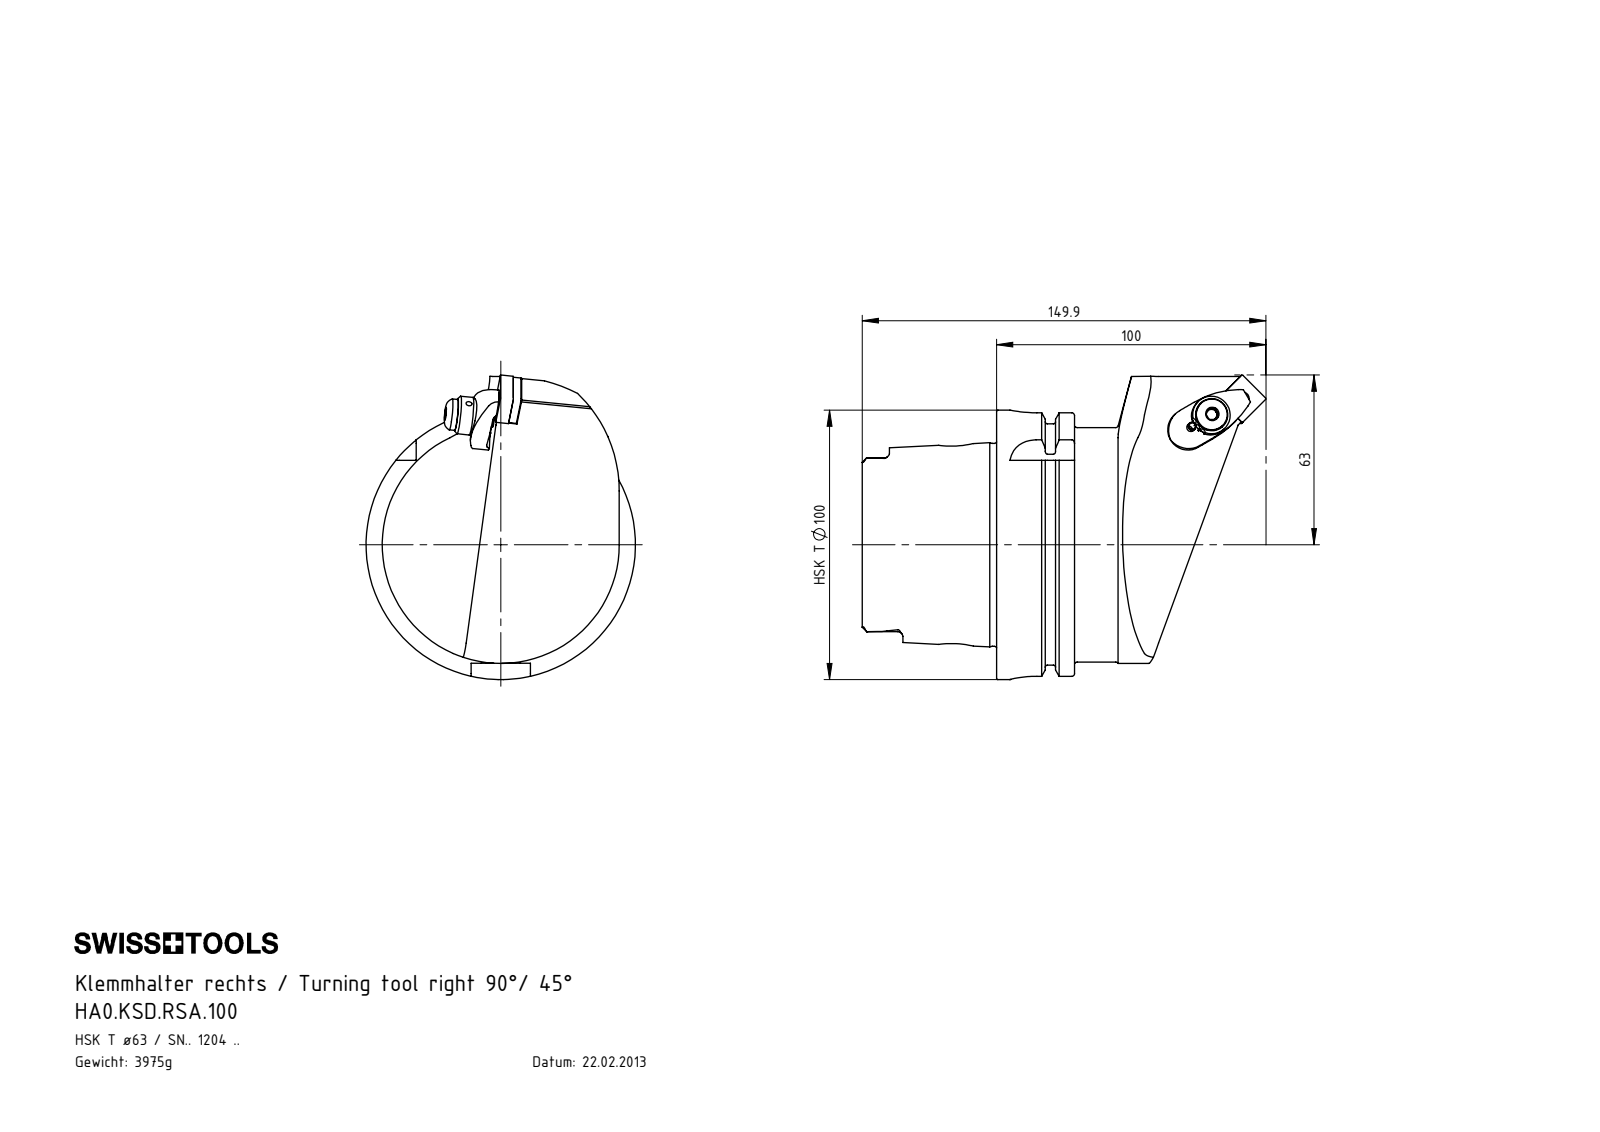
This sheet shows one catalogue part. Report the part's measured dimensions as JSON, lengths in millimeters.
{"part_name": "WSD-ER2.101.003_A; WCC-ER5.102.012_B; WCC-ER2.001.010_A; SNMG120404 (+6 more)", "step_written_by": "SolidWorks 2022 (AUTOMOTIVE_DESIGN)", "units": "millimeters", "bodies": {"solids": 10, "faces": 474, "planar": 119, "cylindrical": 158, "other": 197}, "overall_size": [149.9, 113, 100], "volume_mm3": 505688, "surface_area_mm2": 71838, "round_holes": [[2, 3], [5, 3], [4.2, 2], [6.2, 2], [7, 2], [12, 2], [2.4, 1], [3, 1], [5.16, 1], [6, 1], [6.5, 1], [8.5, 1]], "round_bosses_or_shafts": [[6, 2], [3, 2], [100, 1], [91.95, 1], [87, 1], [75.26, 1], [14, 1], [11.5, 1]], "partial_cylinders_radius": [[0.39, 6], [0.69, 6], [1.9, 6], [0.4, 4], [4.88, 4], [10, 4], [0.8, 3], [1.5, 3]], "face_to_face_distances": [12.45, 28.95, 16.5, 49.9, 62.35, 78.85, 87.8, 78.2, 28.3, 15.85], "hole_center_spacings": [7.99, 8, 8.2, 14.92, 15, 23, 7.47, 7.57]}
